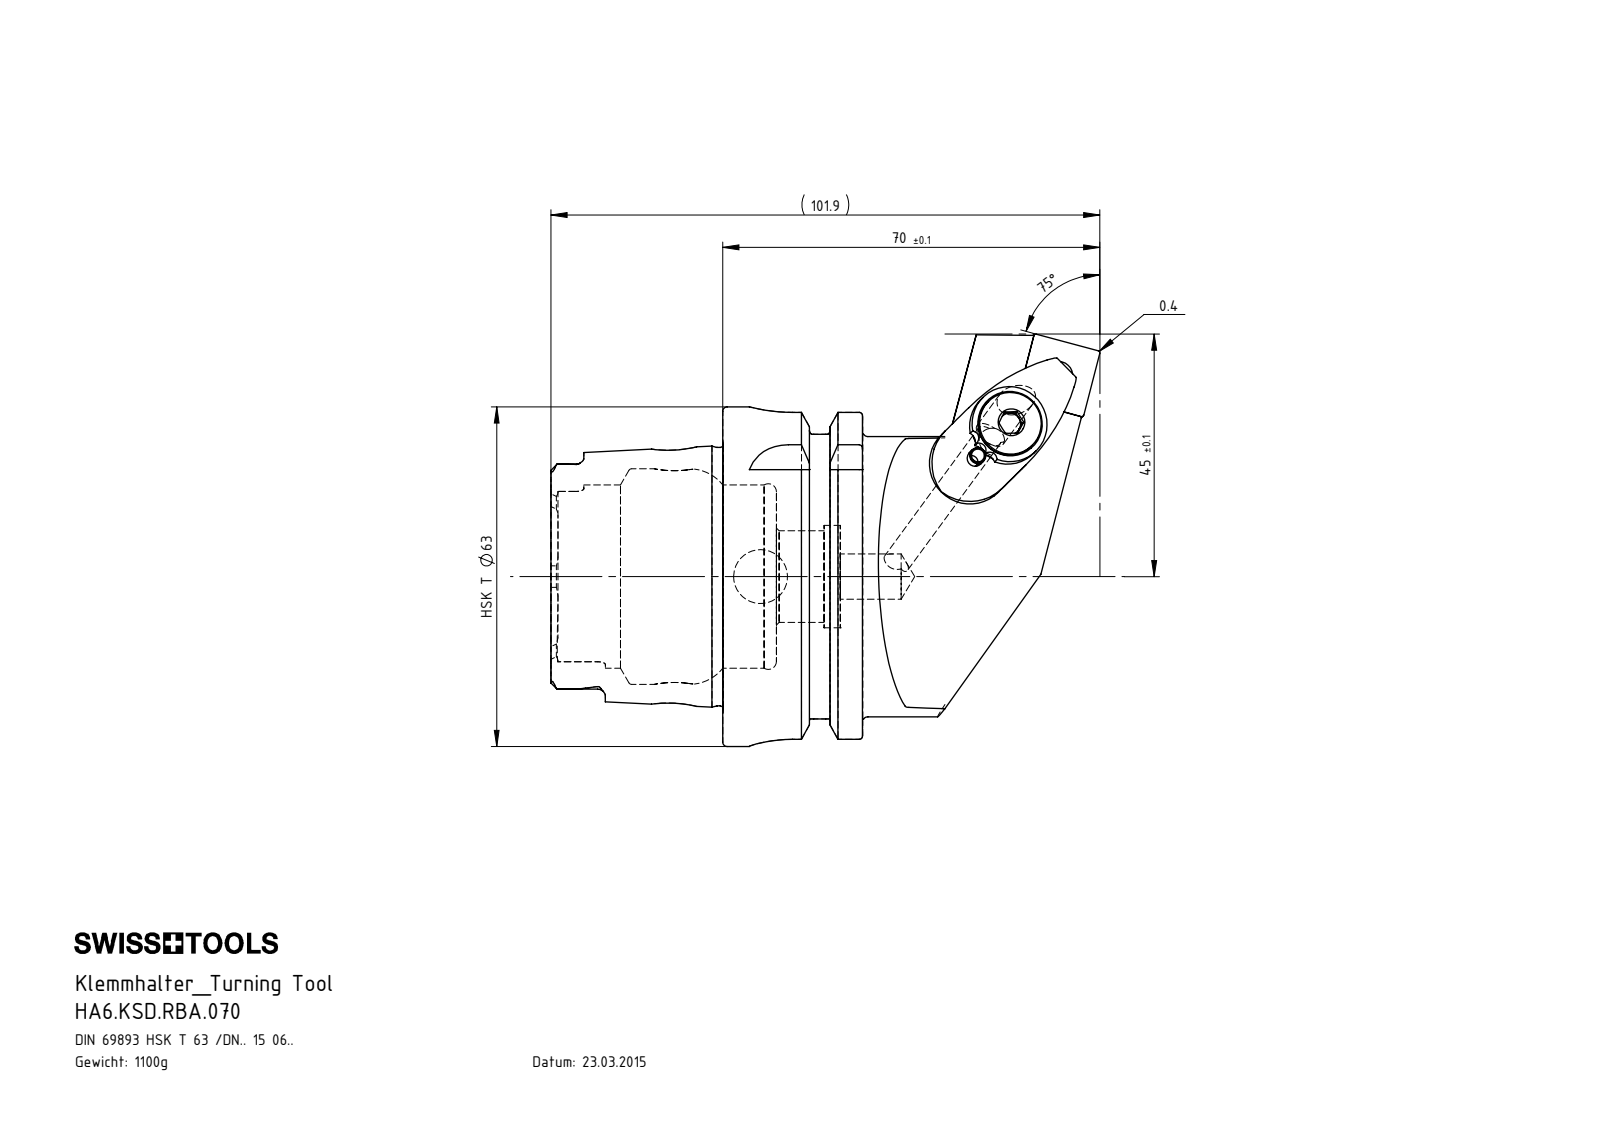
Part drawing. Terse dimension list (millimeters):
name: HA6.KSD.RBA.070; SNMG120404; WCC-ER3.102.024_C; WCC-ER2.001.010_A (+6 more)
written by: SolidWorks 2022 (CONFIG_CONTROL_DESIGN)
unit: mm
bodies: 12 solids, 494 faces (139 planar, 152 cylindrical, 203 other)
size: 101.9 × 76.5 × 63
volume: 141 210 mm³; area: 38 540 mm²
holes: 3× ⌀2, 3× ⌀5, 2× ⌀4.2, 2× ⌀6.2, 1× ⌀2.4, 1× ⌀3, 1× ⌀5.16, 1× ⌀6, 1× ⌀6.5, 1× ⌀7, 1× ⌀7.5, 1× ⌀8.4
bosses: 2× ⌀6, 2× ⌀3, 1× ⌀63, 1× ⌀54.95, 1× ⌀52, 1× ⌀47.94, 1× ⌀14, 1× ⌀11.5
rounds: 6× R0.39, 6× R0.69, 6× R1.4, 4× R0.4, 4× R2.88, 4× R8, 3× R0.8, 3× R1.5
face distances: 0.4, 0.42, 25.95, 16, 9.95, 31.9, 41.85, 57.85, 52.8, 12.4
hole spacings: 8, 15, 23, 7.56, 7.9, 8.2, 14.8, 15.79
